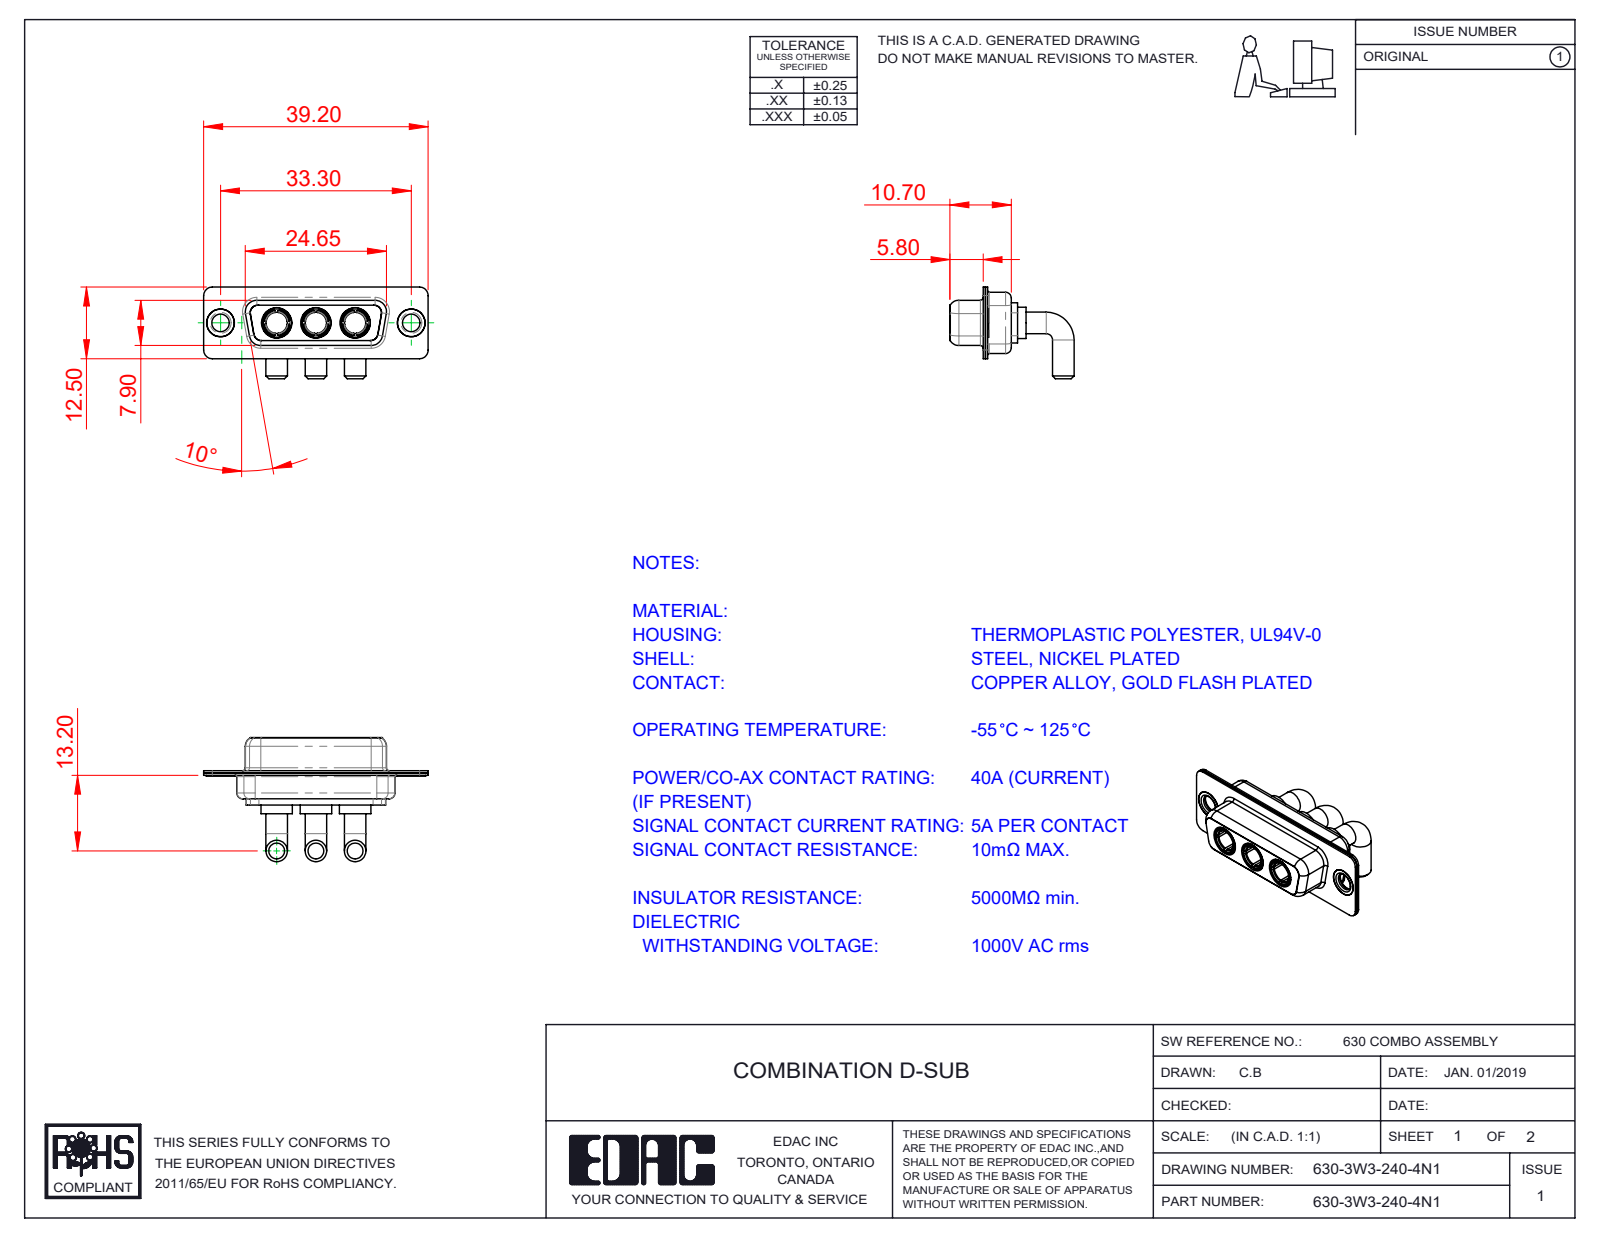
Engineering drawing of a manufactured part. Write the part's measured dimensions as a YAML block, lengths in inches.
part_name: "630Combo Housing_3W3; 630Combo Shell Front_15 Contacts; Power Socket_40A RA; 630Combo Thru Hole Rivet (+2 more)"
step_written_by: "SolidWorks 2020 (CONFIG_CONTROL_DESIGN)"
units: inches
bodies: {solids: 11, faces: 487, planar: 154, cylindrical: 196, other: 137}
overall_size: [1.543, 0.854, 0.63]
volume: 0.17
surface_area: 9.162
round_holes:
  - {diameter: 0.191, count: 5}
  - {diameter: 0.146, count: 3}
  - {diameter: 0.209, count: 3}
  - {diameter: 0.12, count: 2}
  - {diameter: 0.157, count: 2}
  - {diameter: 0.159, count: 2}
round_bosses_or_shafts:
  - {diameter: 0.148, count: 6}
  - {diameter: 0.217, count: 3}
  - {diameter: 0.205, count: 3}
  - {diameter: 0.195, count: 3}
  - {diameter: 0.187, count: 3}
  - {diameter: 0.197, count: 2}
  - {diameter: 0.195, count: 2}
  - {diameter: 0.189, count: 2}
partial_cylinders:
  - {radius: 0.059, count: 16}
  - {radius: 0.053, count: 12}
  - {radius: 0.079, count: 12}
  - {radius: 0.063, count: 8}
  - {radius: 0.01, count: 4}
  - {radius: 0.02, count: 4}
  - {radius: 0.024, count: 4}
  - {radius: 0.026, count: 4}
face_to_face_distances: [0.016, 0.018, 0.055, 0.333, 0.35, 0.071, 0.244, 0.031, 0.278, 0.073]
hole_center_spacings: [0.27, 0.386, 0.656, 0.925, 0.539, 1.311]
